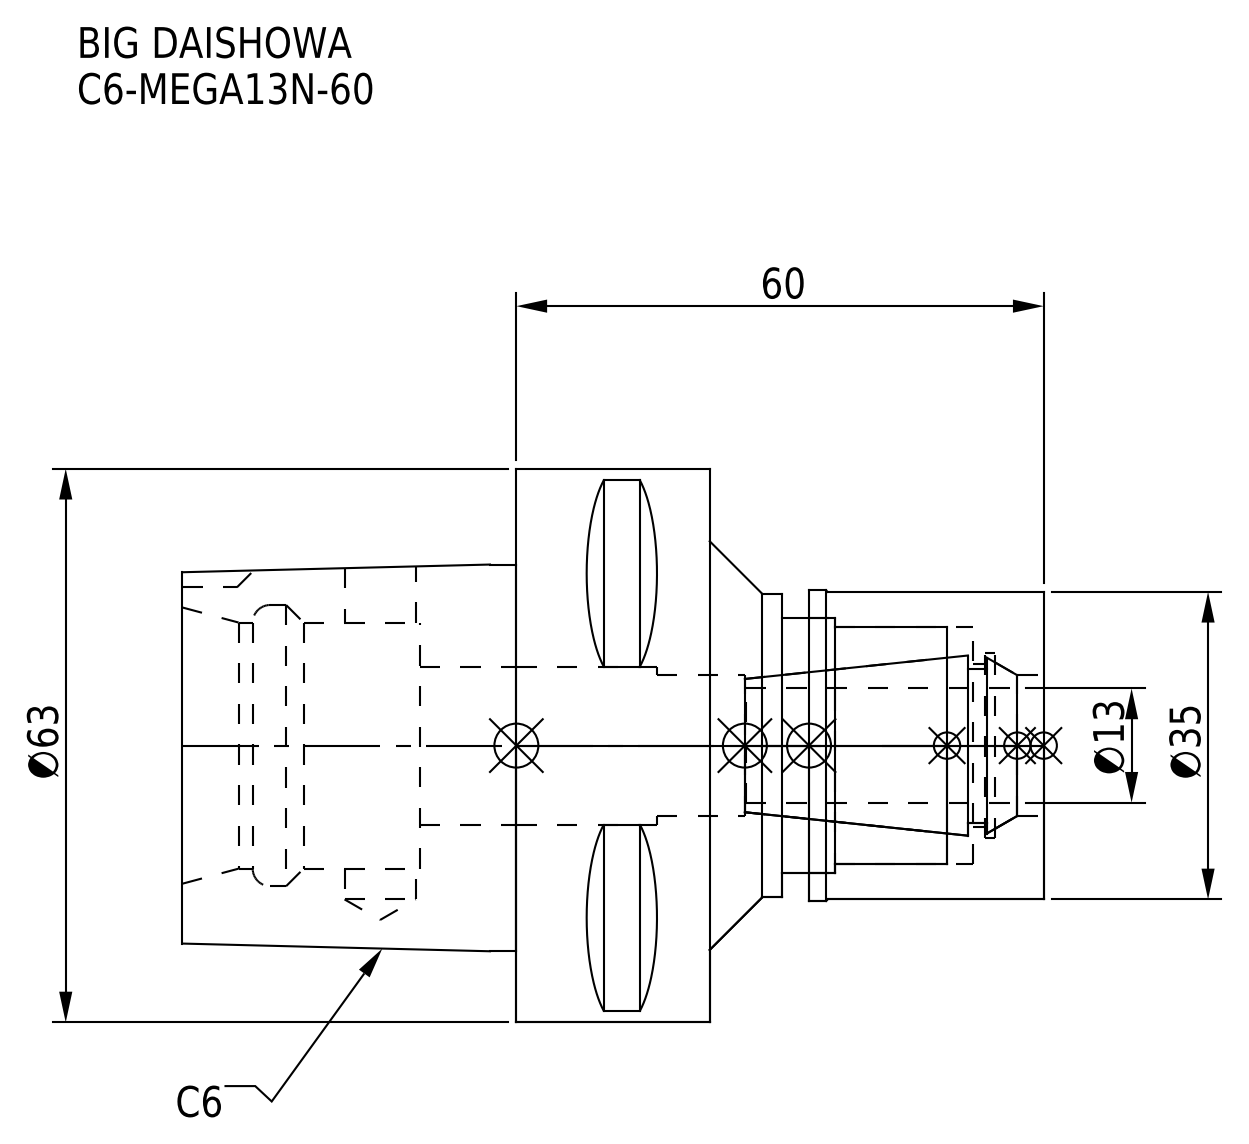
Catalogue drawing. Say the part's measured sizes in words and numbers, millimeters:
The part is named "C6-MEGA13N-60-130_ASM.stp; MGN13_1.stp; C6-MEGA13N-60_1.stp; C6-MEGA13N-60-130.stp (+3 more)". Its 3-D file was written by "SolidWorks 2019 (CONFIG_CONTROL_DESIGN)". It is 2 solids with 92 faces: 37 planar, 37 cylindrical and 18 other. Overall it measures 98 by 63 by 63 millimeters. Its volume is 122 868 cubic millimeters and its surface area 30 244 square millimeters. Round holes: 1 of diameter 8.1, 1 of diameter 16, 1 of diameter 18, 1 of diameter 18.5, 1 of diameter 21, 1 of diameter 27, 1 of diameter 28, 1 of diameter 29, 1 of diameter 32. Round bosses or shafts: 1 of diameter 63, 1 of diameter 35.3, 1 of diameter 35, 1 of diameter 34.5. Partial cylindrical surfaces (rounded edges, fillets, slot ends): 1 of radius 5. The main face-to-face distances are 60, 22, 38, 27, 11, 98, 33, 71, 26.7, 11.3.
